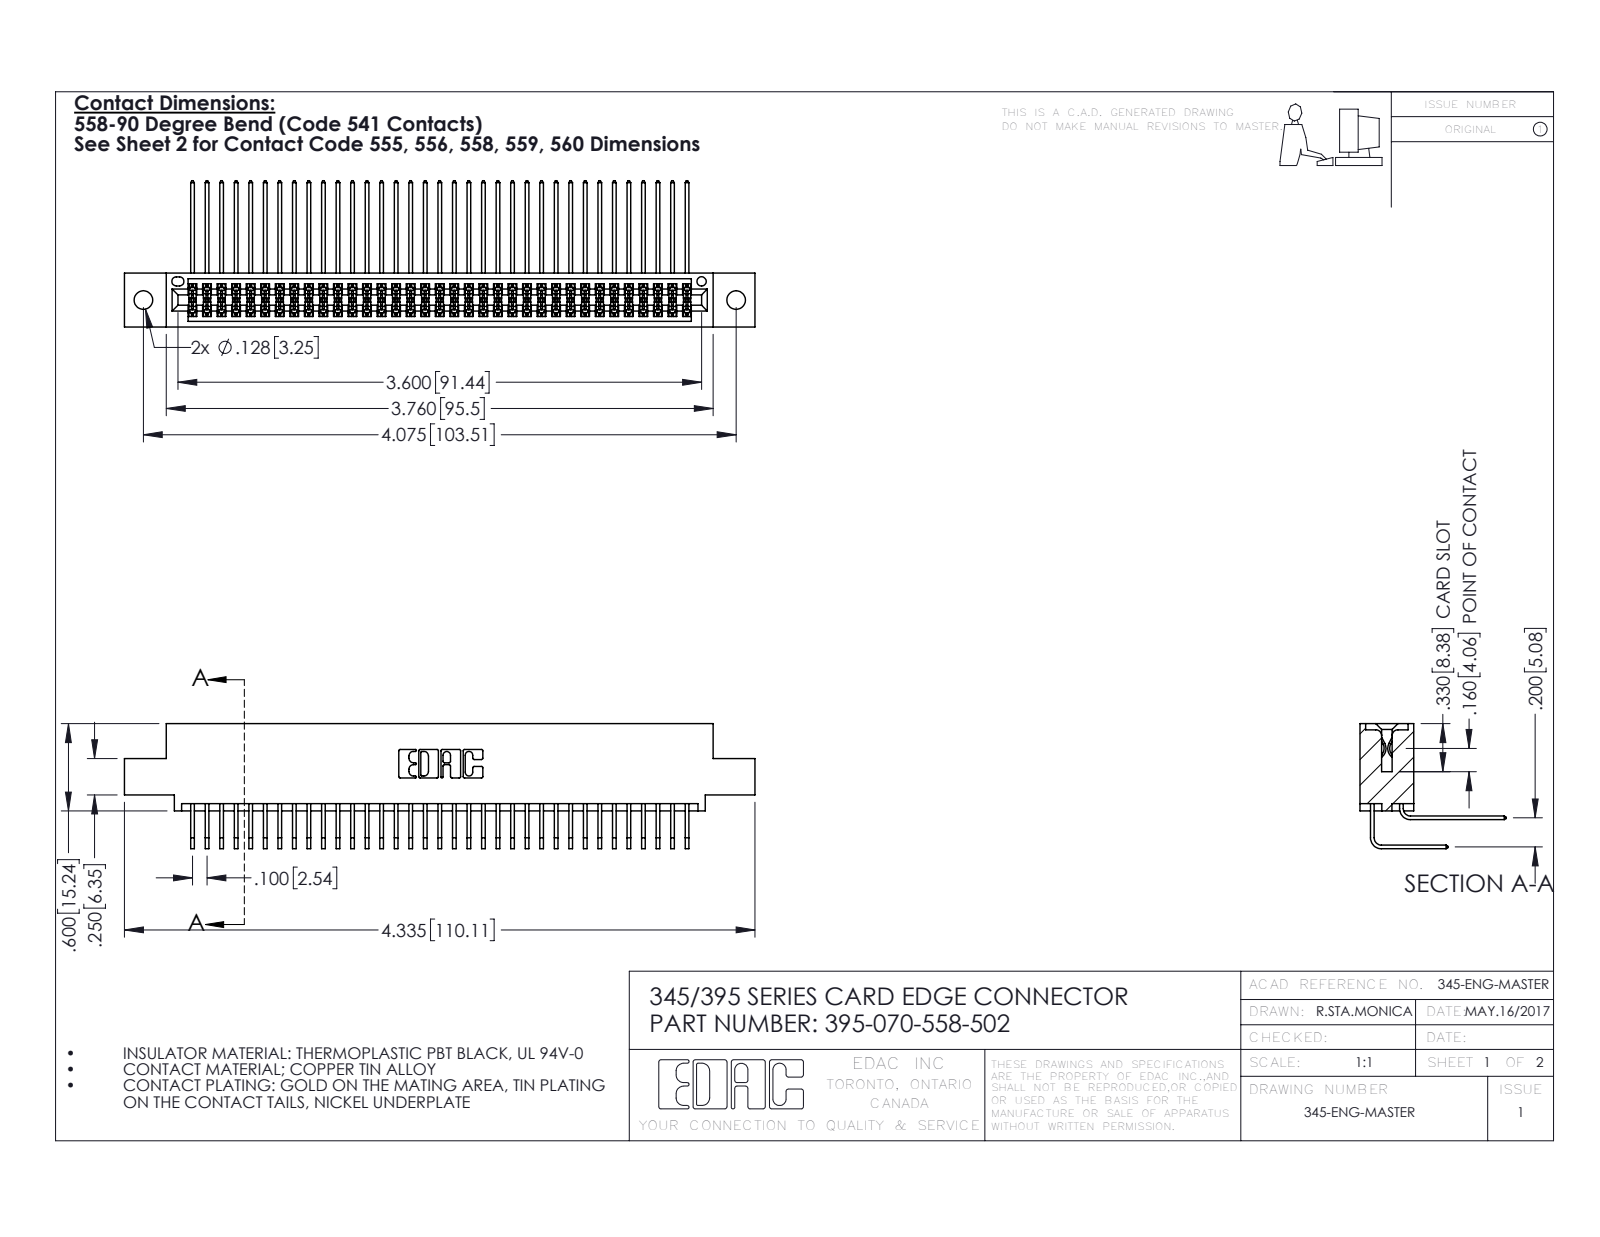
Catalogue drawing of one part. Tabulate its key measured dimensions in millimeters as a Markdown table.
| quantity | value |
| --- | --- |
| part name | 345 Part_0.110 Offset - 0.128 Dia; 345-292-001_558 Tail - 2; 345-292-001_558 559 Tail - 1; 395-070-558-502 |
| STEP written by | SolidWorks 2016 (CONFIG_CONTROL_DESIGN) |
| units | millimeters |
| bodies | 71 solids, 3770 faces (2534 planar, 1236 cylindrical, 0 other) |
| overall size | 110.1 × 25.5 × 21.8 |
| volume | 10 900 mm³ |
| surface area | 17 730 mm² |
| round holes (diameter × count) | 3.3 × 2, 1.6 × 1 |
| partial cylindrical surfaces (radius × count) | 0.2 × 106, 0.3 × 22, 0.2 × 6, 0.8 × 6, 0.7 × 3, 0.4 × 2, 0.5 × 2, 0.6 × 2 |
| main face-to-face distances | 1.8, 7.6, 5.1, 9.4, 2.5, 6.9, 0.6, 5.7, 0.6, 4.4 |
| hole center spacings | 6.9, 97.5, 103.5 |
